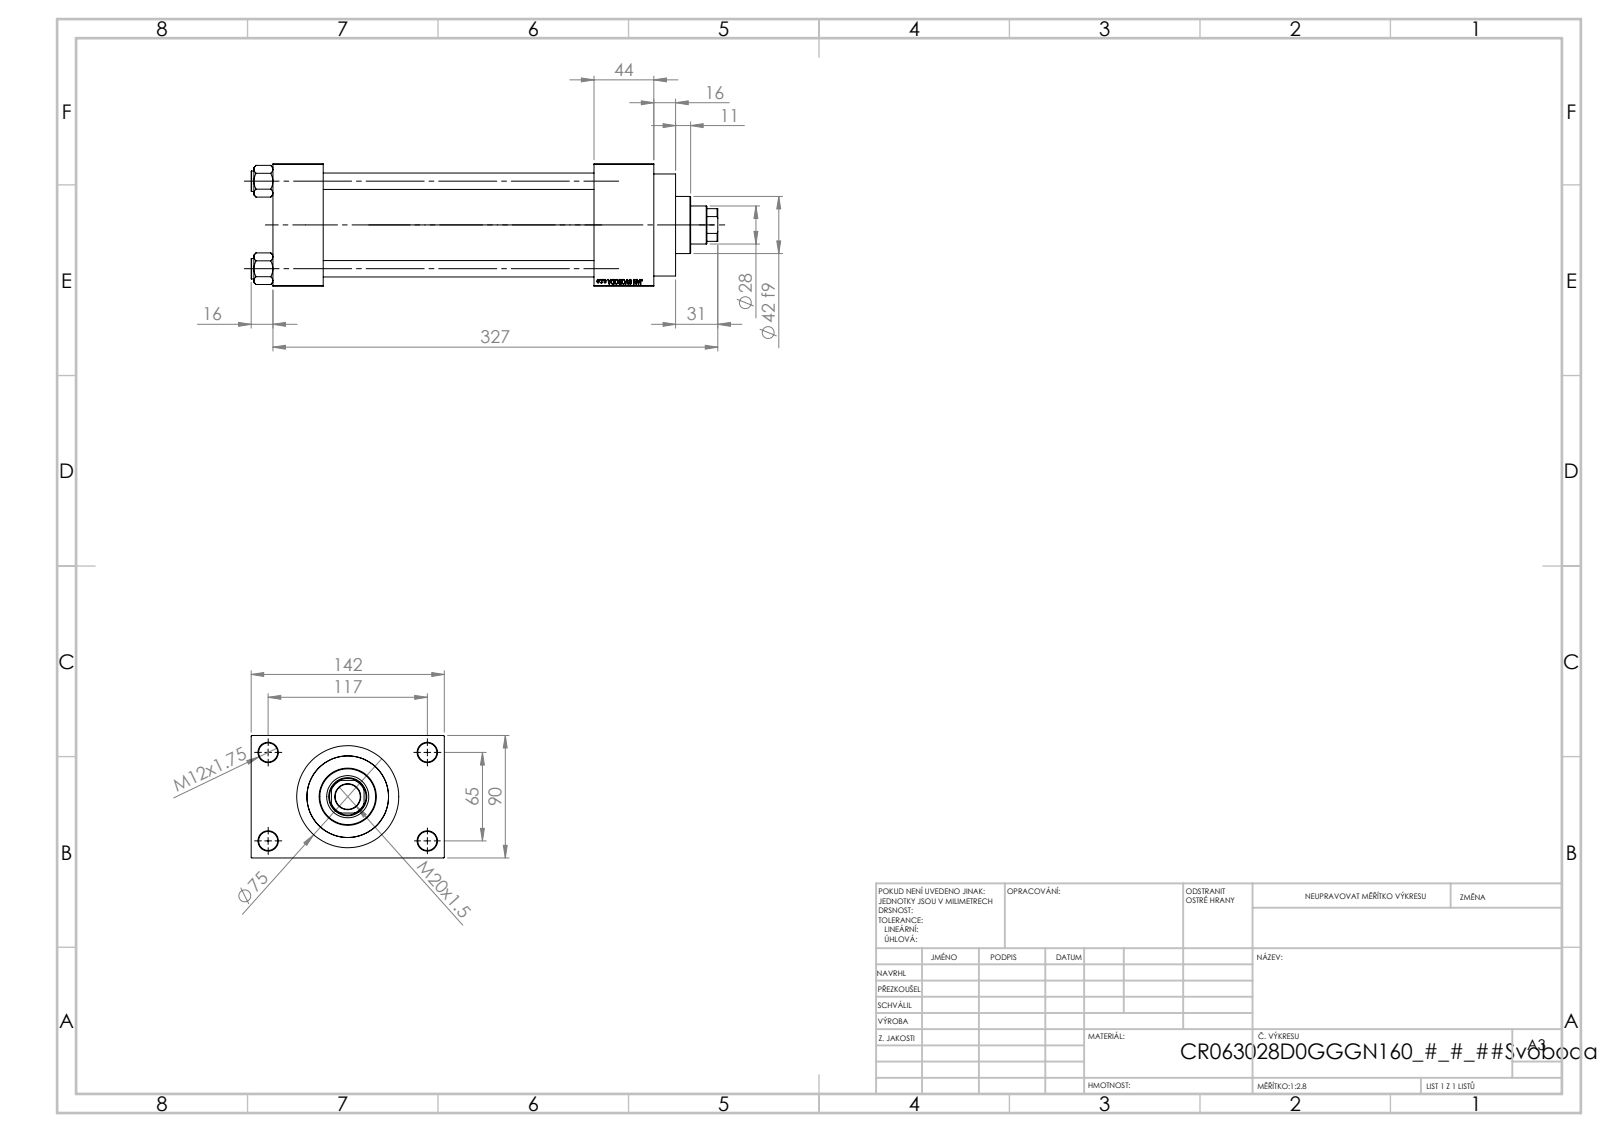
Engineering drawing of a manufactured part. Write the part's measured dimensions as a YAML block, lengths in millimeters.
part_name: "V215CR_D_TYCINKA; V215_VC_A; V215CR_D_Body; NUT_M5_D (+1 more)"
step_written_by: "SolidWorks 2019 (CONFIG_CONTROL_DESIGN)"
units: millimeters
bodies: {solids: 11, faces: 1104, planar: 497, cylindrical: 89, other: 518}
overall_size: [343, 142, 90]
volume: 1342000
surface_area: 290090
round_holes:
  - {diameter: 12, count: 4}
  - {diameter: 14, count: 4}
  - {diameter: 7, count: 2}
  - {diameter: 20.96, count: 2}
  - {diameter: 30, count: 2}
  - {diameter: 18.5, count: 1}
  - {diameter: 28, count: 1}
  - {diameter: 31, count: 1}
  - {diameter: 50, count: 1}
  - {diameter: 60, count: 1}
  - {diameter: 63, count: 1}
round_bosses_or_shafts:
  - {diameter: 15, count: 4}
  - {diameter: 75, count: 1}
  - {diameter: 69, count: 1}
  - {diameter: 42, count: 1}
partial_cylinders:
  - {radius: 13.5, count: 1}
face_to_face_distances: [90, 199, 37, 236, 243, 280, 44, 26, 116, 142]
hole_center_spacings: [26.35, 45.47, 64.3, 66.92, 69.81, 90.65, 111.34, 65]
